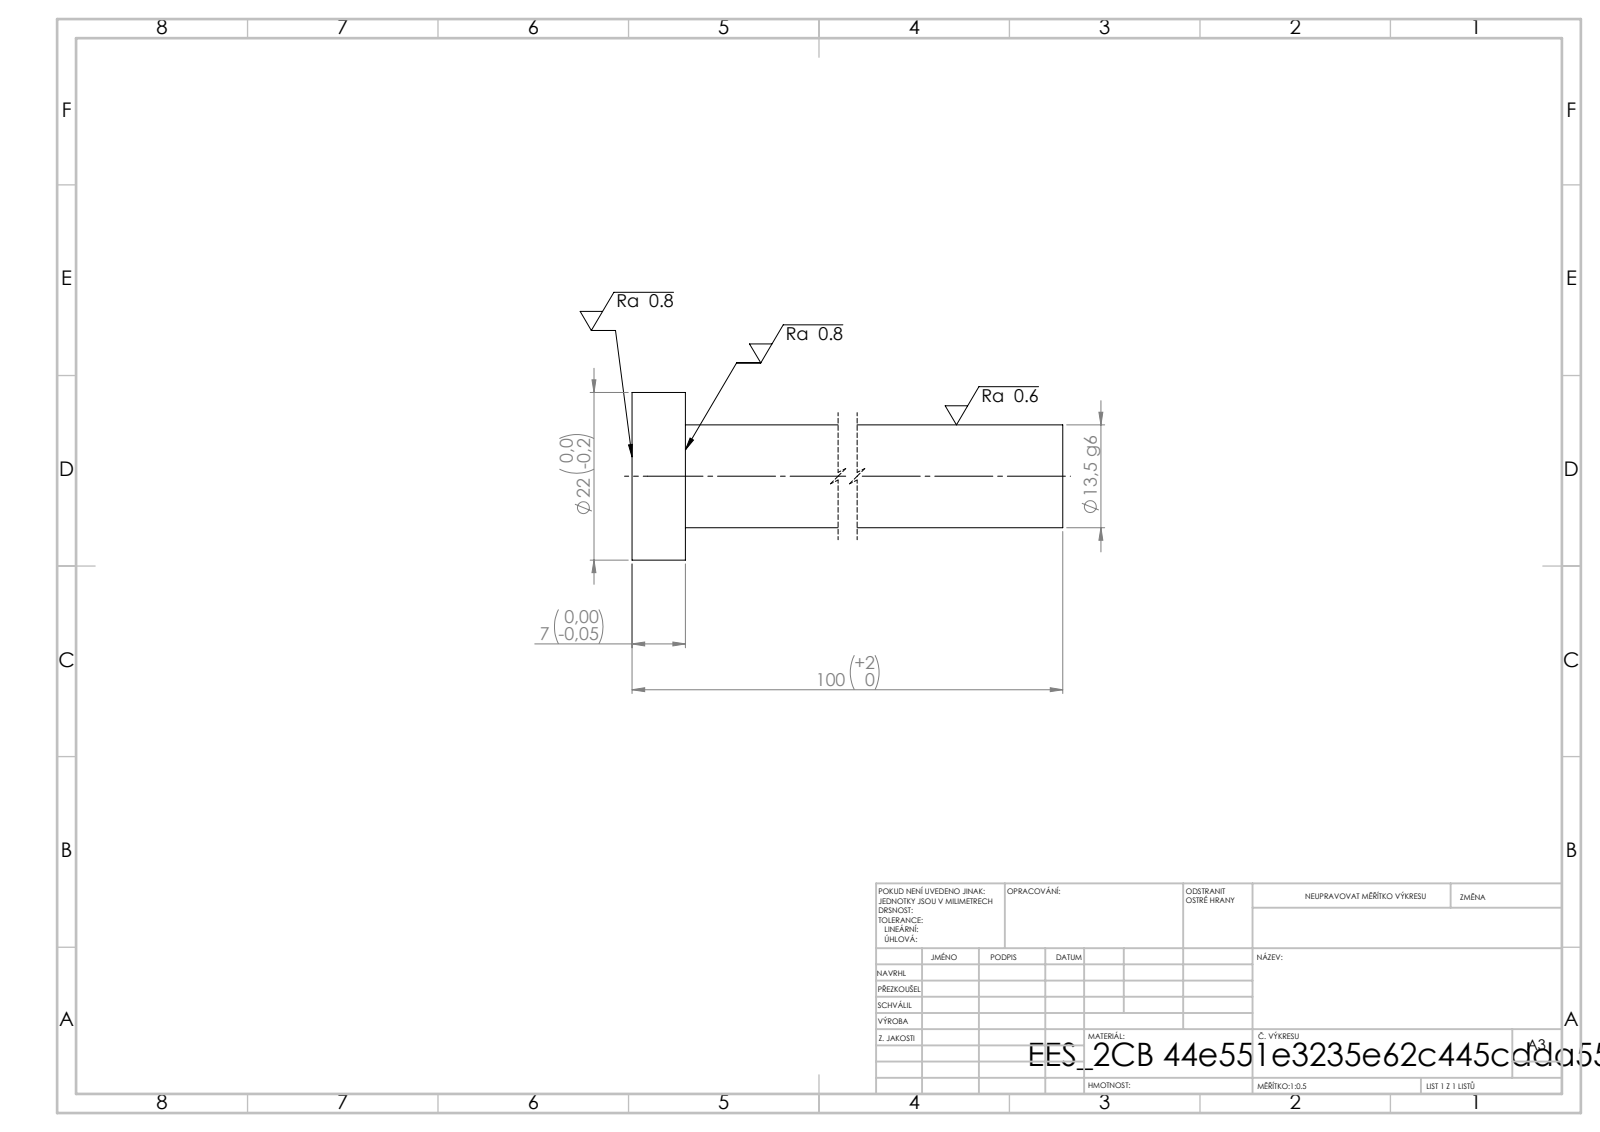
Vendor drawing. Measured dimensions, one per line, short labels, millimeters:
written by: SolidWorks 2019 (CONFIG_CONTROL_DESIGN)
unit: mm
bodies: 1 solid, 7 faces (3 planar, 4 cylindrical, 0 other)
size: 100 × 22 × 22
volume: 15 973 mm³; area: 5 188 mm²
bosses: 1× ⌀22, 1× ⌀13.5
face distances: 7, 100, 93
